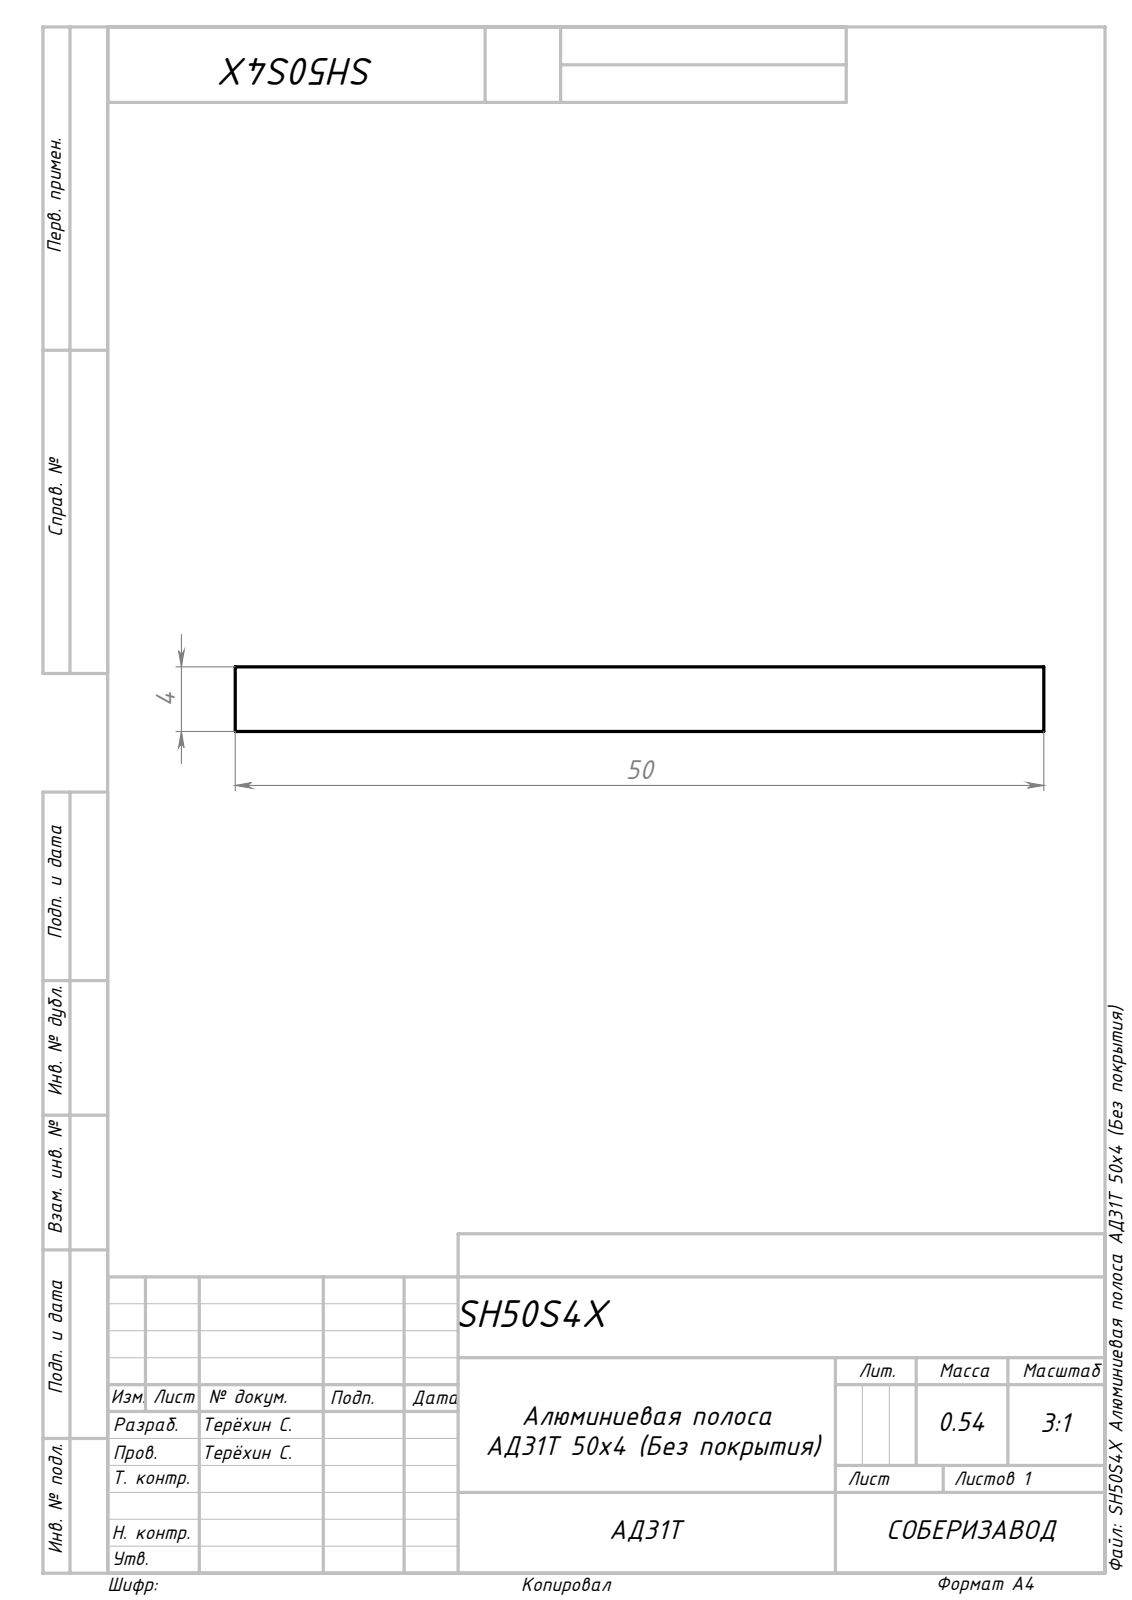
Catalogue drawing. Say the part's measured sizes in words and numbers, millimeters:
The part is named "Сборка11; SH50S4X Алюминиевая полоса АД31Т 50х4 (Без покрытия)_50х4". Its 3-D file was written by "SolidWorks 2024 (AUTOMOTIVE_DESIGN)". It is 1 solid with 6 faces: 6 planar, 0 cylindrical and 0 other. Overall it measures 1000 by 50 by 4 millimeters. Its volume is 200 000 cubic millimeters and its surface area 108 400 square millimeters. The main face-to-face distances are 4, 50, 1000.
